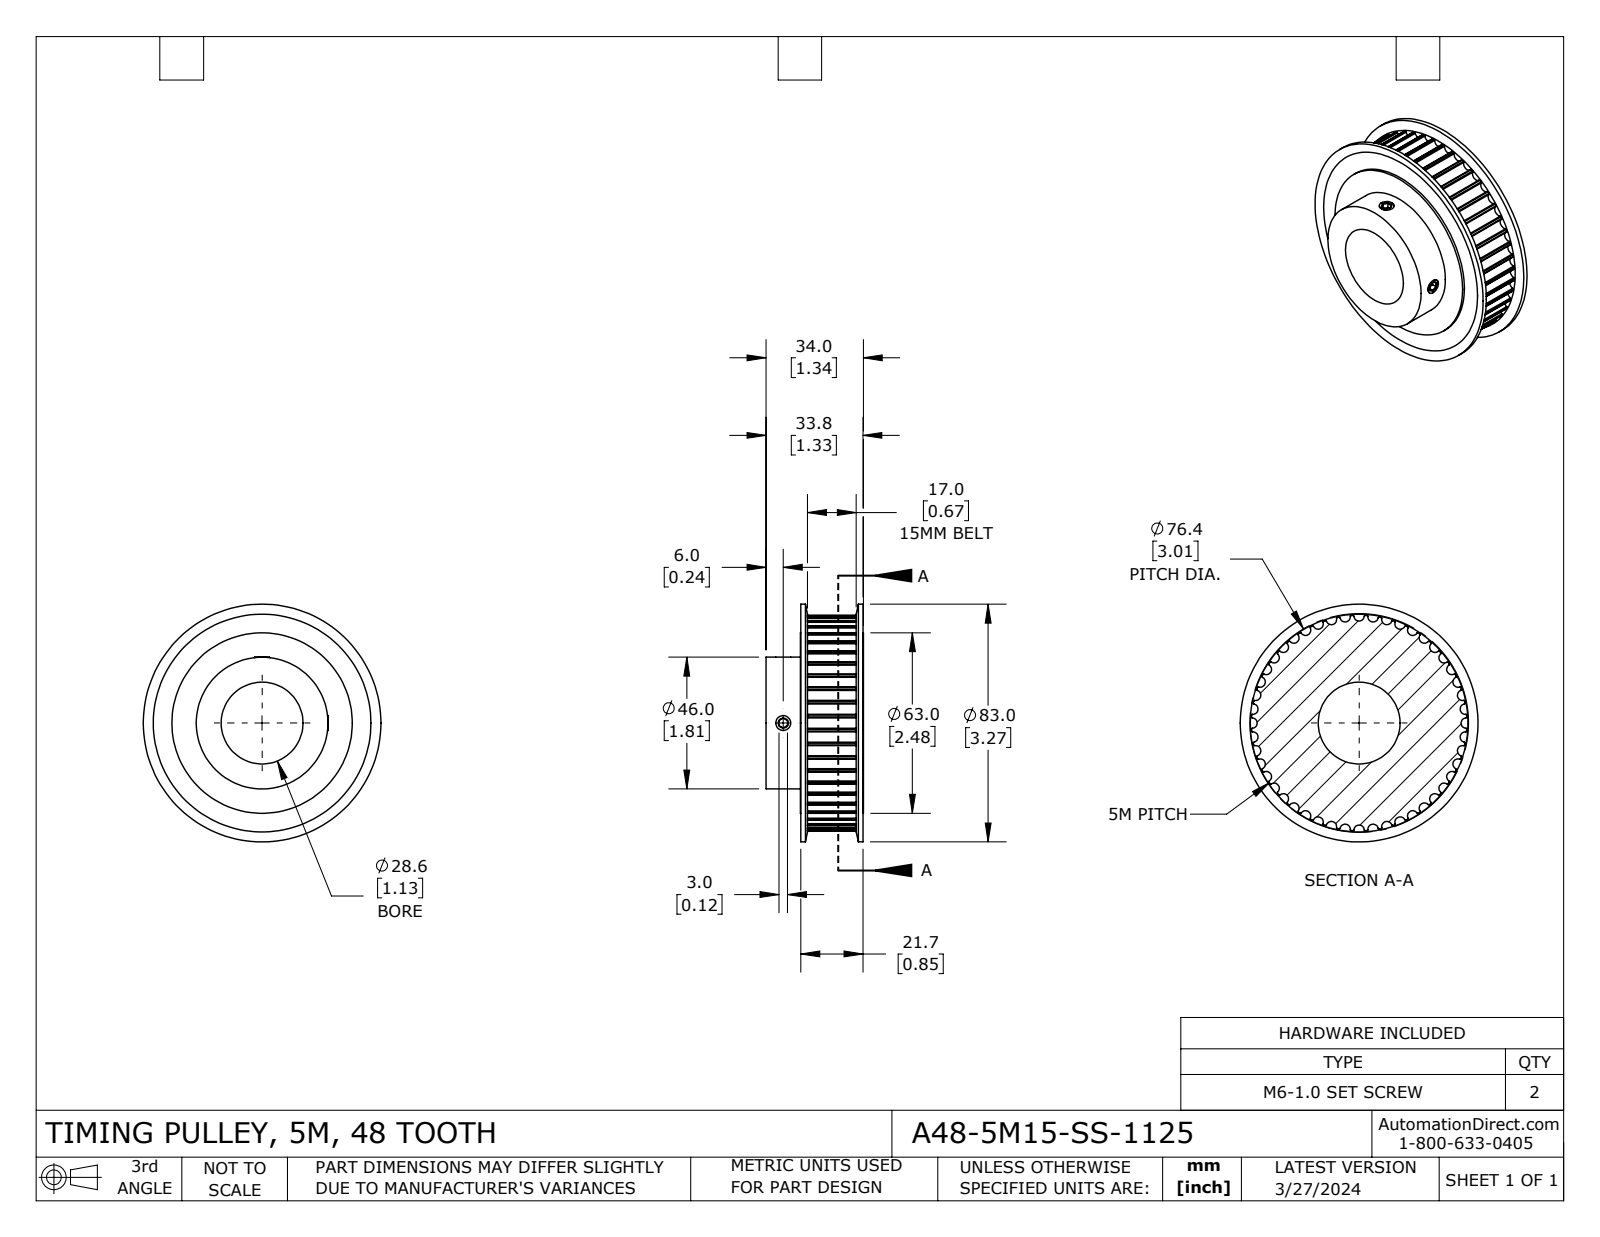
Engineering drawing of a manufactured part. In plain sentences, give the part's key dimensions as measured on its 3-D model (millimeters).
The part is named "A48-5M15-SS-1125". Its 3-D file was written by "SolidWorks 2021 (CONFIG_CONTROL_DESIGN)". It is 5 solids with 322 faces: 25 planar, 263 cylindrical and 34 other. Overall it measures 83 by 83 by 34 millimeters. Its volume is 91 724 cubic millimeters and its surface area 29 785 square millimeters. Round holes: 2 of diameter 5, 1 of diameter 28.58, 1 of diameter 63. Round bosses or shafts: 2 of diameter 6, 1 of diameter 83, 1 of diameter 46. Partial cylindrical surfaces (rounded edges, fillets, slot ends): 96 of radius 0.3, 48 of radius 1.82, 1 of radius 37.62. The main face-to-face distances are 19.5, 2.5, 0.9, 21.1, 1.6, 18.6, 17, 22, 20.2, 34.
